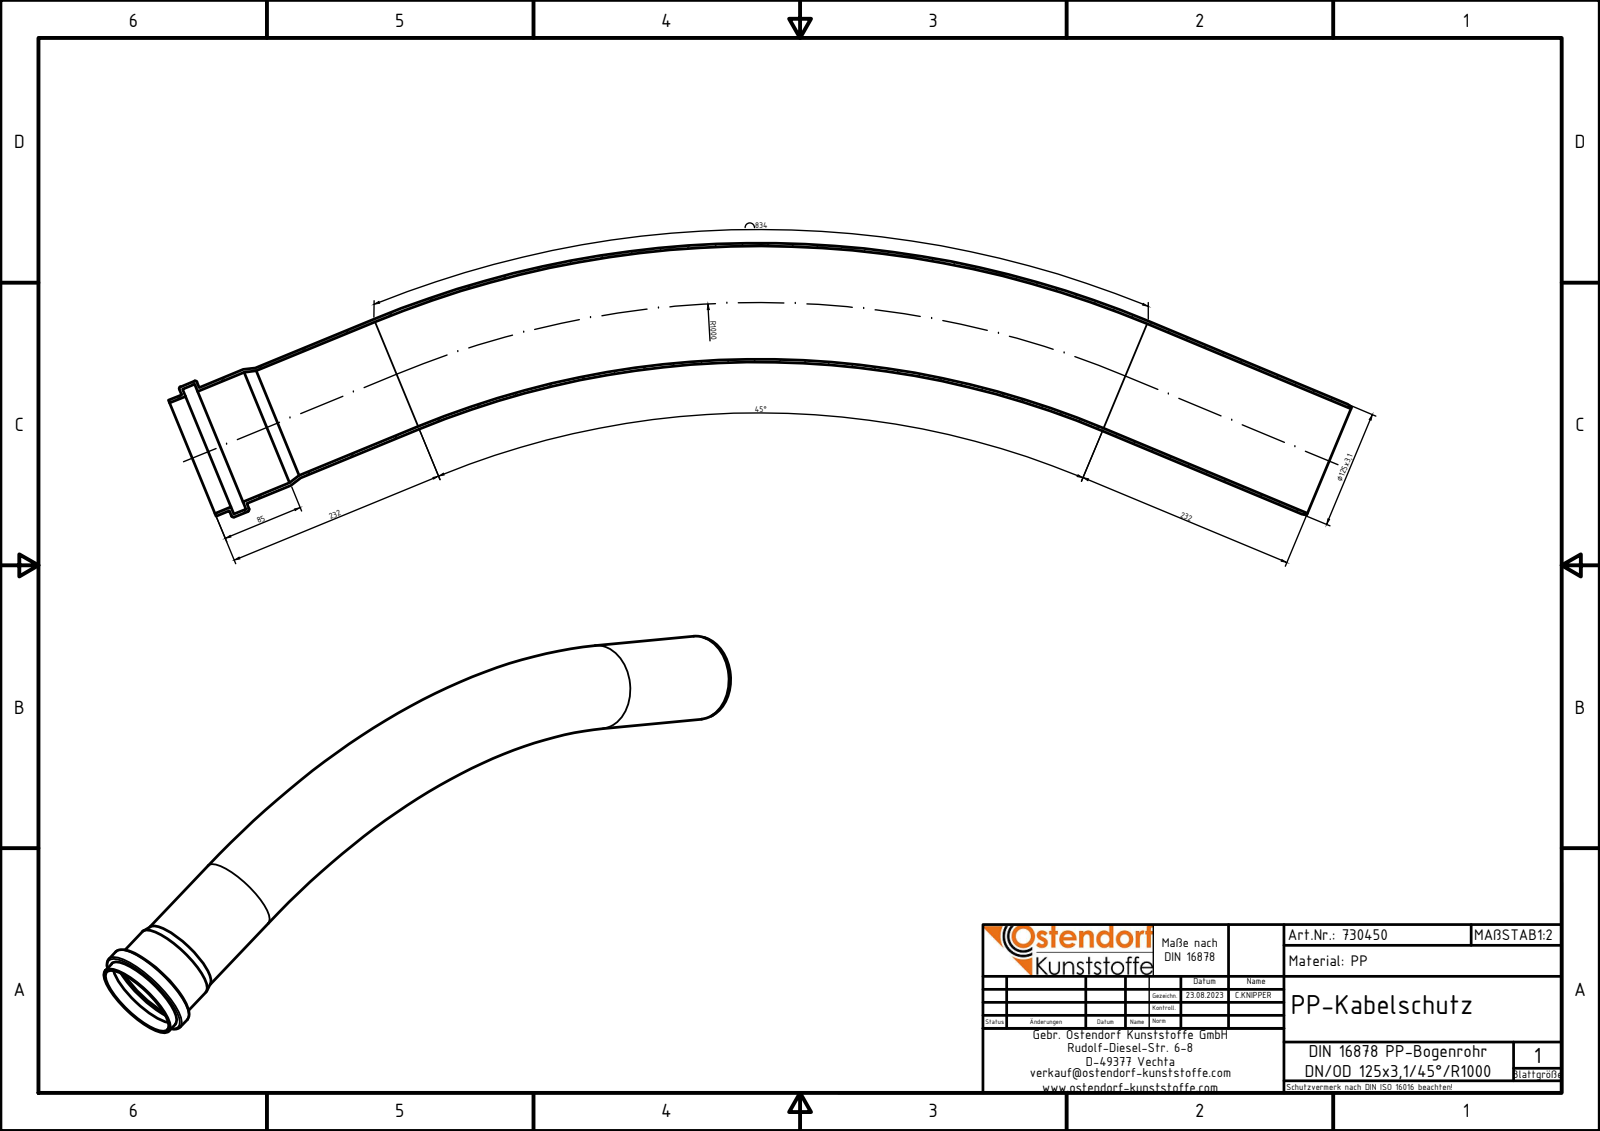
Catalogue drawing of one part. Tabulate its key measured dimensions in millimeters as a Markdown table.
| quantity | value |
| --- | --- |
| part name | PP-Bogenrohr_125x31_R1000_45_SM_35019_730450 |
| STEP written by | Autodesk Inventor 2024 (AUTOMOTIVE_DESIGN) |
| units | millimeters |
| bodies | 1 solid, 23 faces (6 planar, 10 cylindrical, 7 other) |
| overall size | 1146.4 × 574.19 × 148 |
| volume | 1 512 000 mm³ |
| surface area | 978 044 mm² |
| round holes (diameter × count) | 118.8 × 2, 125.4 × 1, 141.8 × 1 |
| round bosses / shafts (diameter × count) | 125 × 2, 148 × 1, 131.6 × 1 |
| main face-to-face distances | 3.1, 16.9, 13.8, 20, 15, 18.1, 31.9, 35 |
